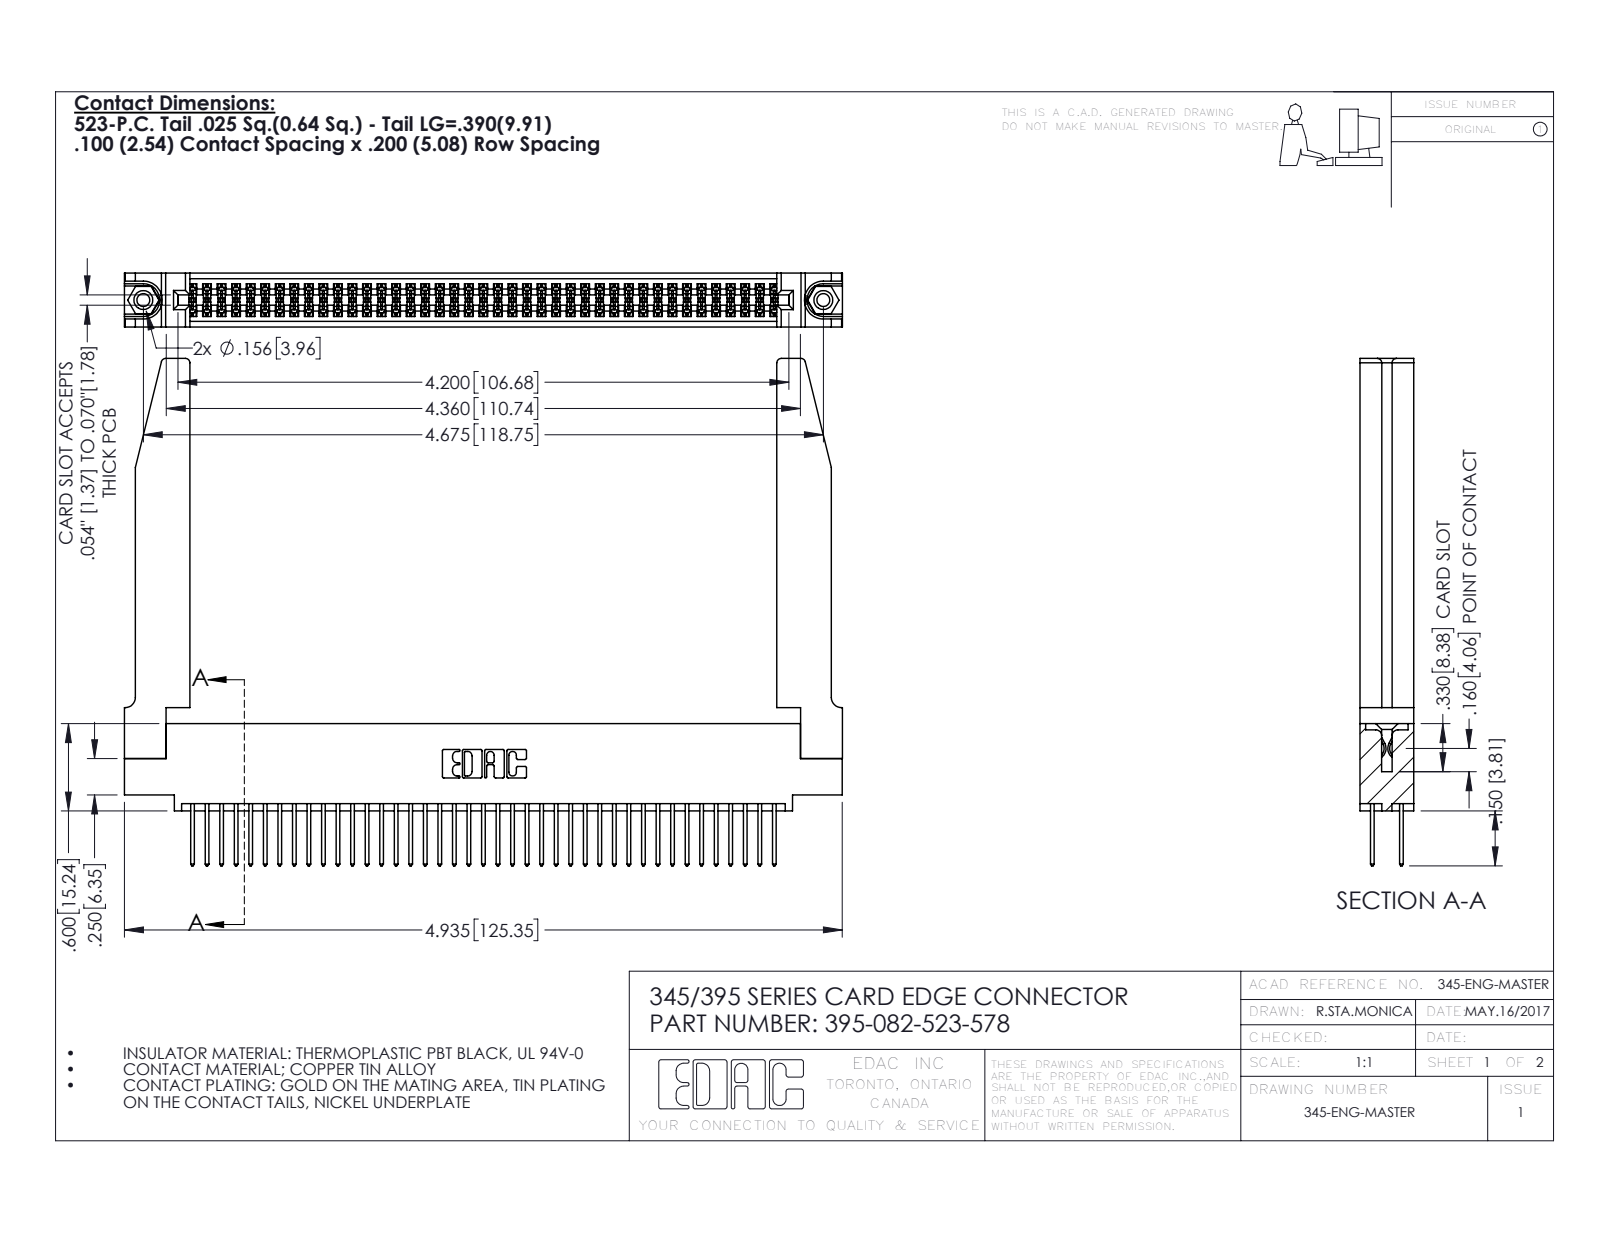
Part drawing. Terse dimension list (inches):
name: 345-250-001_345-250-001-102; 345 Part_0.110 Offset - 0.156 Dia-TH; 345-292-001_345-293-123; 395-082-523-578 (+1 more)
written by: SolidWorks 2016 (CONFIG_CONTROL_DESIGN)
unit: in
bodies: 87 solids, 4464 faces (2932 planar, 1480 cylindrical, 52 other)
size: 4.936 × 3.487 × 0.37
volume: 1.223 in³; area: 39.98 in²
holes: 2× ⌀0.089, 2× ⌀0.125, 2× ⌀0.156, 1× ⌀0.064
bosses: 2× ⌀0.155
rounds: 123× R0.006, 82× R0.01, 22× R0.01, 8× R0.03, 6× R0.007, 6× R0.031, 3× R0.026, 2× R0.014
face distances: 0.072, 0.298, 0.37, 0.2, 0.098, 0.272, 0.025, 0.225, 0.175, 0.148
hole spacings: 0.27, 4.439, 4.675
